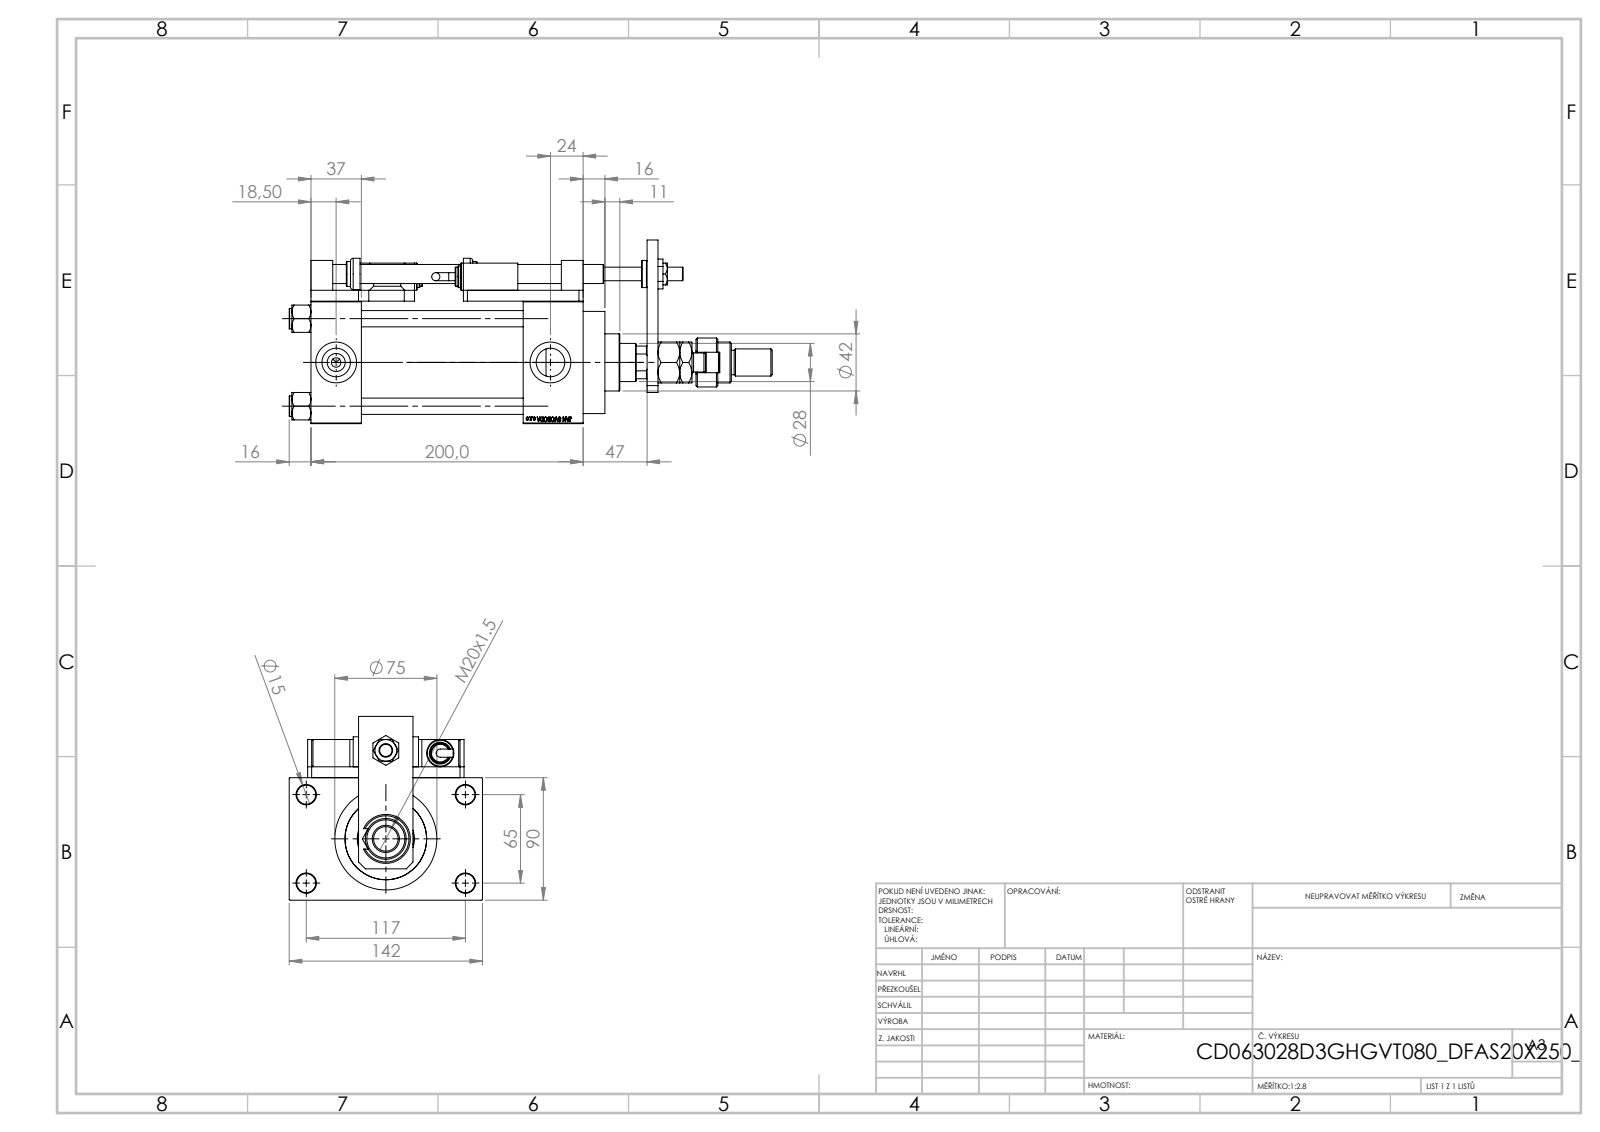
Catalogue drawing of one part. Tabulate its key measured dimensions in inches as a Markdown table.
| quantity | value |
| --- | --- |
| part name | V215CD_VC_A; FEMALE_PART_FOR_DFA; V215CD_SWITCH_Q_MAGNET; V215CD_C_DFAS_SWITCH (+7 more) |
| STEP written by | SolidWorks 2019 (CONFIG_CONTROL_DESIGN) |
| units | inches |
| bodies | 28 solids, 1517 faces (694 planar, 180 cylindrical, 643 other) |
| overall size | 13.976 × 5.591 × 5.315 |
| volume | 92.51 in³ |
| surface area | 535.2 in² |
| round holes (diameter × count) | 0.551 × 5, 0.335 × 4, 0.472 × 4, 0.531 × 4, 0.825 × 4, 1.181 × 4, 0.276 × 3, 0.394 × 1, 0.728 × 1, 0.787 × 1, 1.102 × 1, 1.22 × 1 |
| round bosses / shafts (diameter × count) | 0.591 × 4, 0.787 × 3, 0.551 × 3, 0.63 × 2, 0.236 × 2, 2.953 × 1, 2.717 × 1, 1.654 × 1 |
| partial cylindrical surfaces (radius × count) | 0.295 × 5, 0.472 × 1, 0.531 × 1 |
| main face-to-face distances | 0.315, 3.543, 1.732, 1.457, 7.874, 3.858, 6.417, 6.142, 4.685, 1.85 |
| hole center spacings | 2.635, 1.037, 1.79, 2.531, 2.748, 3.569, 4.383, 2.559 |
